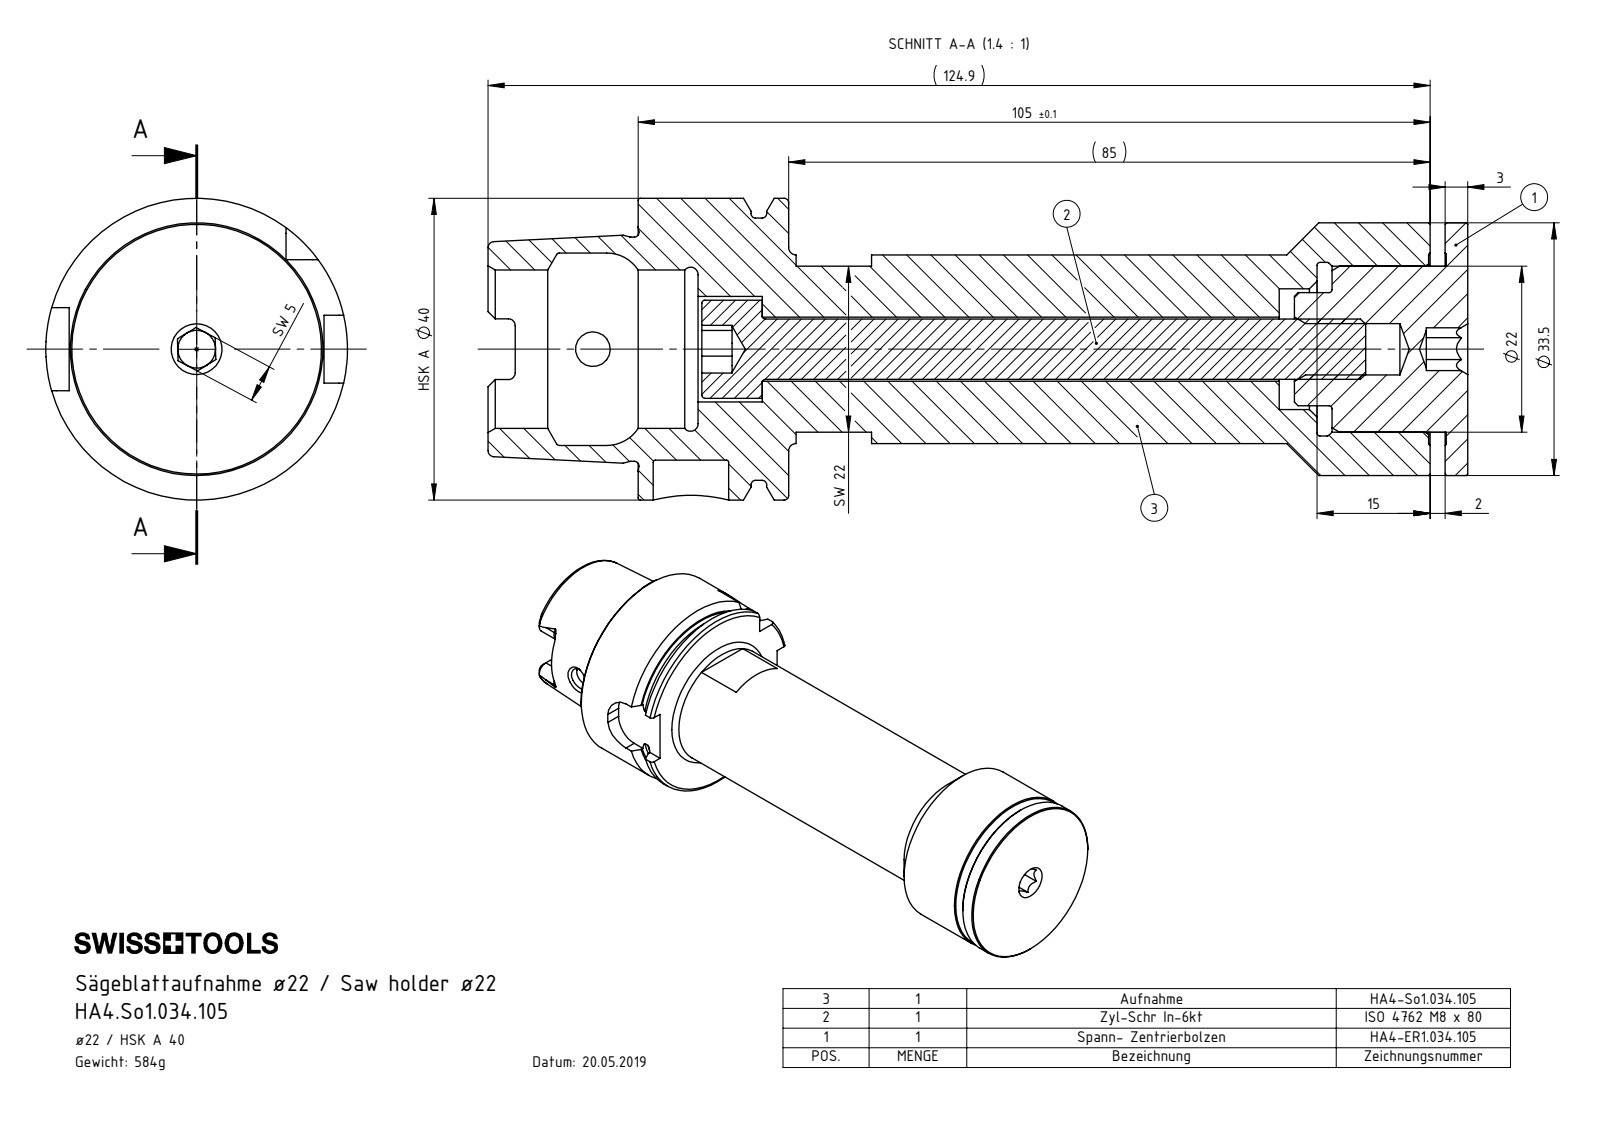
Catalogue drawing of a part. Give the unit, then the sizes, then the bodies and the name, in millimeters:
Units: millimetres
Overall size (bounding box): 129.9 × 40 × 40
Round holes (diameter × count): ⌀4.6 ×1, ⌀6.8 ×1, ⌀8.5 ×1, ⌀10 ×1, ⌀14 ×1, ⌀16 ×1, ⌀21 ×1, ⌀22 ×1, ⌀23 ×1, ⌀25.5 ×1
Round bosses / shafts (diameter × count): ⌀40 ×1, ⌀34.75 ×1, ⌀33.5 ×1, ⌀29.71 ×1, ⌀25 ×1, ⌀15 ×1, ⌀13 ×1, ⌀8 ×1
Partial cylindrical surfaces — rounded edges, fillets, slot ends (radius × count): R0.9 ×6, R1.88 ×4, R4.5 ×4
Main face-to-face distances: 5, 2, 90.05, 3, 19.95, 110, 20, 107, 87.05, 105
Volume: 74 449 mm³ · Surface area: 26 577 mm²
Bodies: 3 solids, 191 faces (84 planar, 41 cylindrical, 66 other)
Part name (STEP PRODUCT): HA4-So1.034.105_A_Fertigbearbeitung; HA4.So1.034.105; HA4-ER1.034.105_A; ISO 4762 - M8 x 80_PreviewCfg
STEP written by: SolidWorks 2017 (AUTOMOTIVE_DESIGN)
